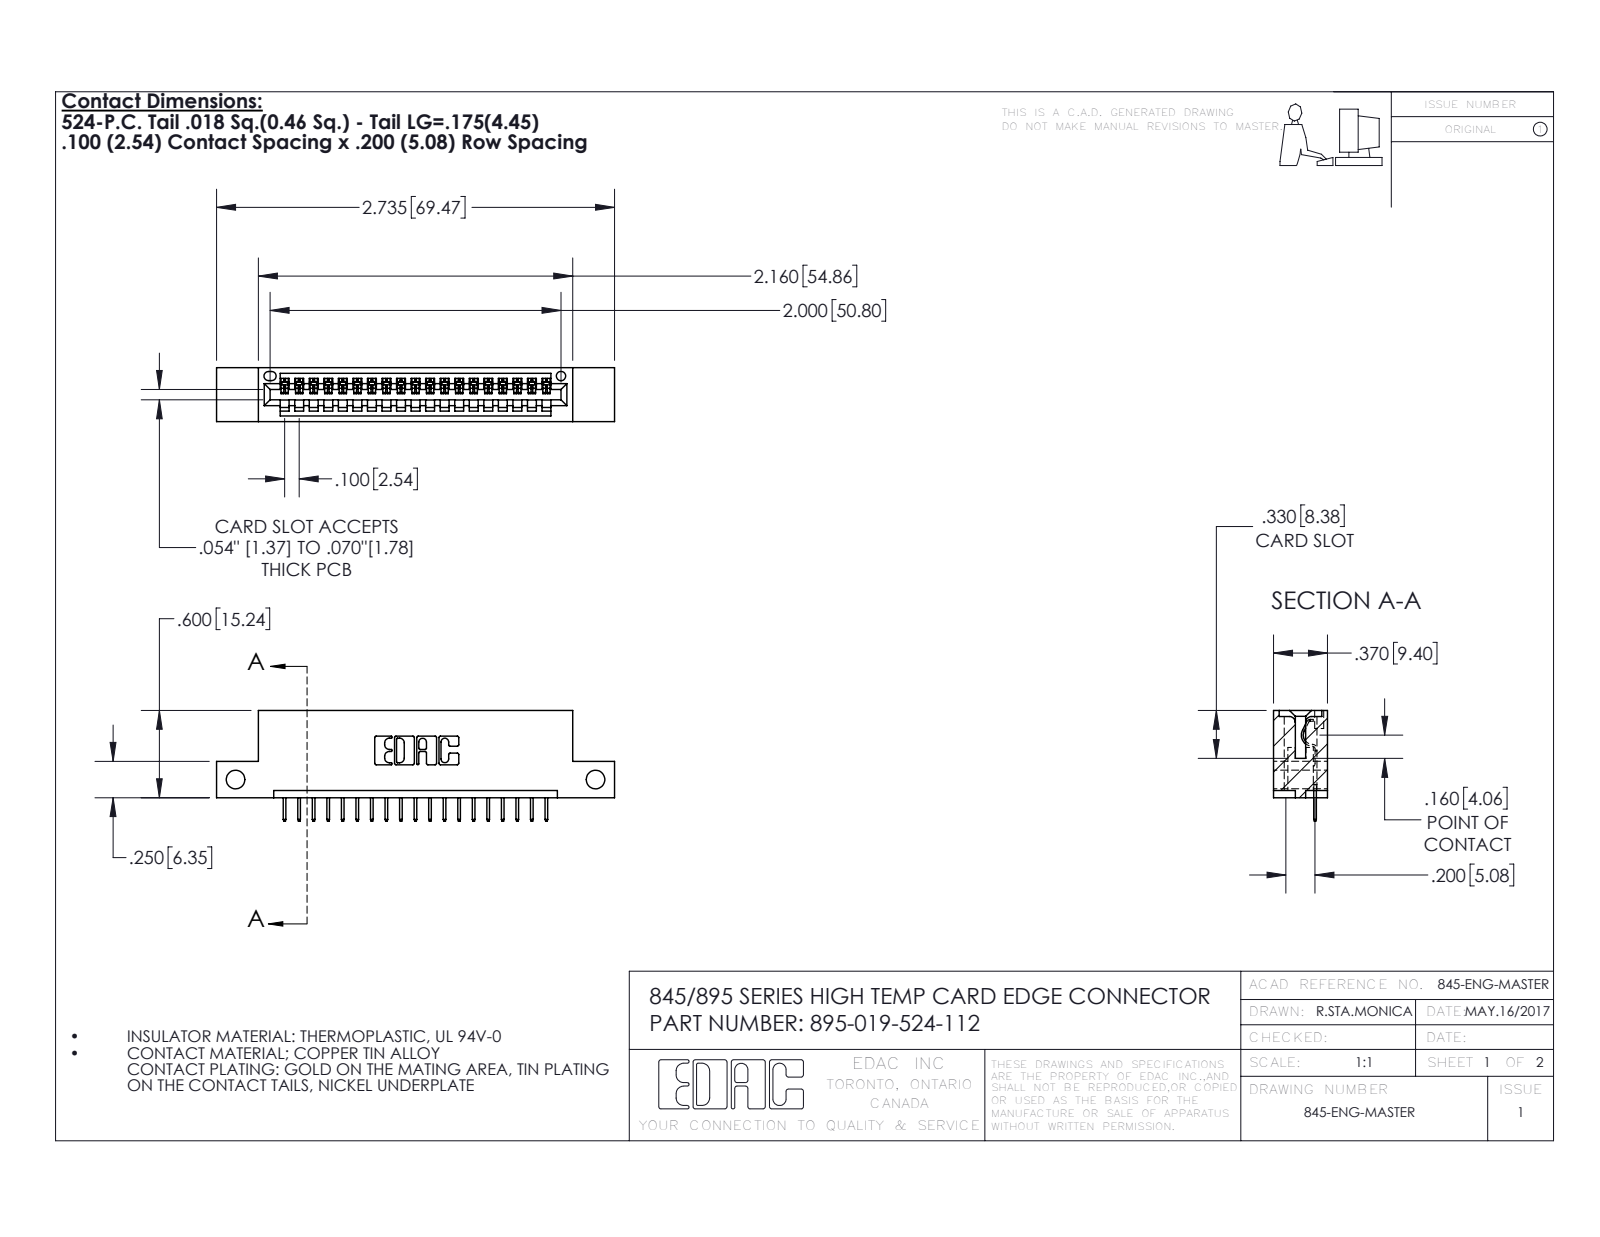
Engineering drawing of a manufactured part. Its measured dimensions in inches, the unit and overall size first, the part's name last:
Units: inches
Overall size (bounding box): 2.735 × 0.762 × 0.37
Round holes (diameter × count): ⌀0.128 ×2, ⌀0.064 ×1
Partial cylindrical surfaces — rounded edges, fillets, slot ends (radius × count): R0.006 ×38, R0.01 ×22, R0.007 ×6, R0.031 ×6, R0.026 ×3, R0.031 ×2, R0.04 ×2, R0.014 ×1
Main face-to-face distances: 0.072, 0.298, 0.2, 0.37, 0.098, 0.272, 0.025, 0.225, 0.072, 0.6
Hole centre spacings: 2.475
Volume: 0.381 in³ · Surface area: 11.79 in²
Bodies: 20 solids, 1304 faces (954 planar, 350 cylindrical, 0 other)
Part name (STEP PRODUCT): 345 Part_Flush Mounting Lugs - Side Mount; 345-292-001_345-293-124; 395-019-524-112
STEP written by: SolidWorks 2016 (CONFIG_CONTROL_DESIGN)
